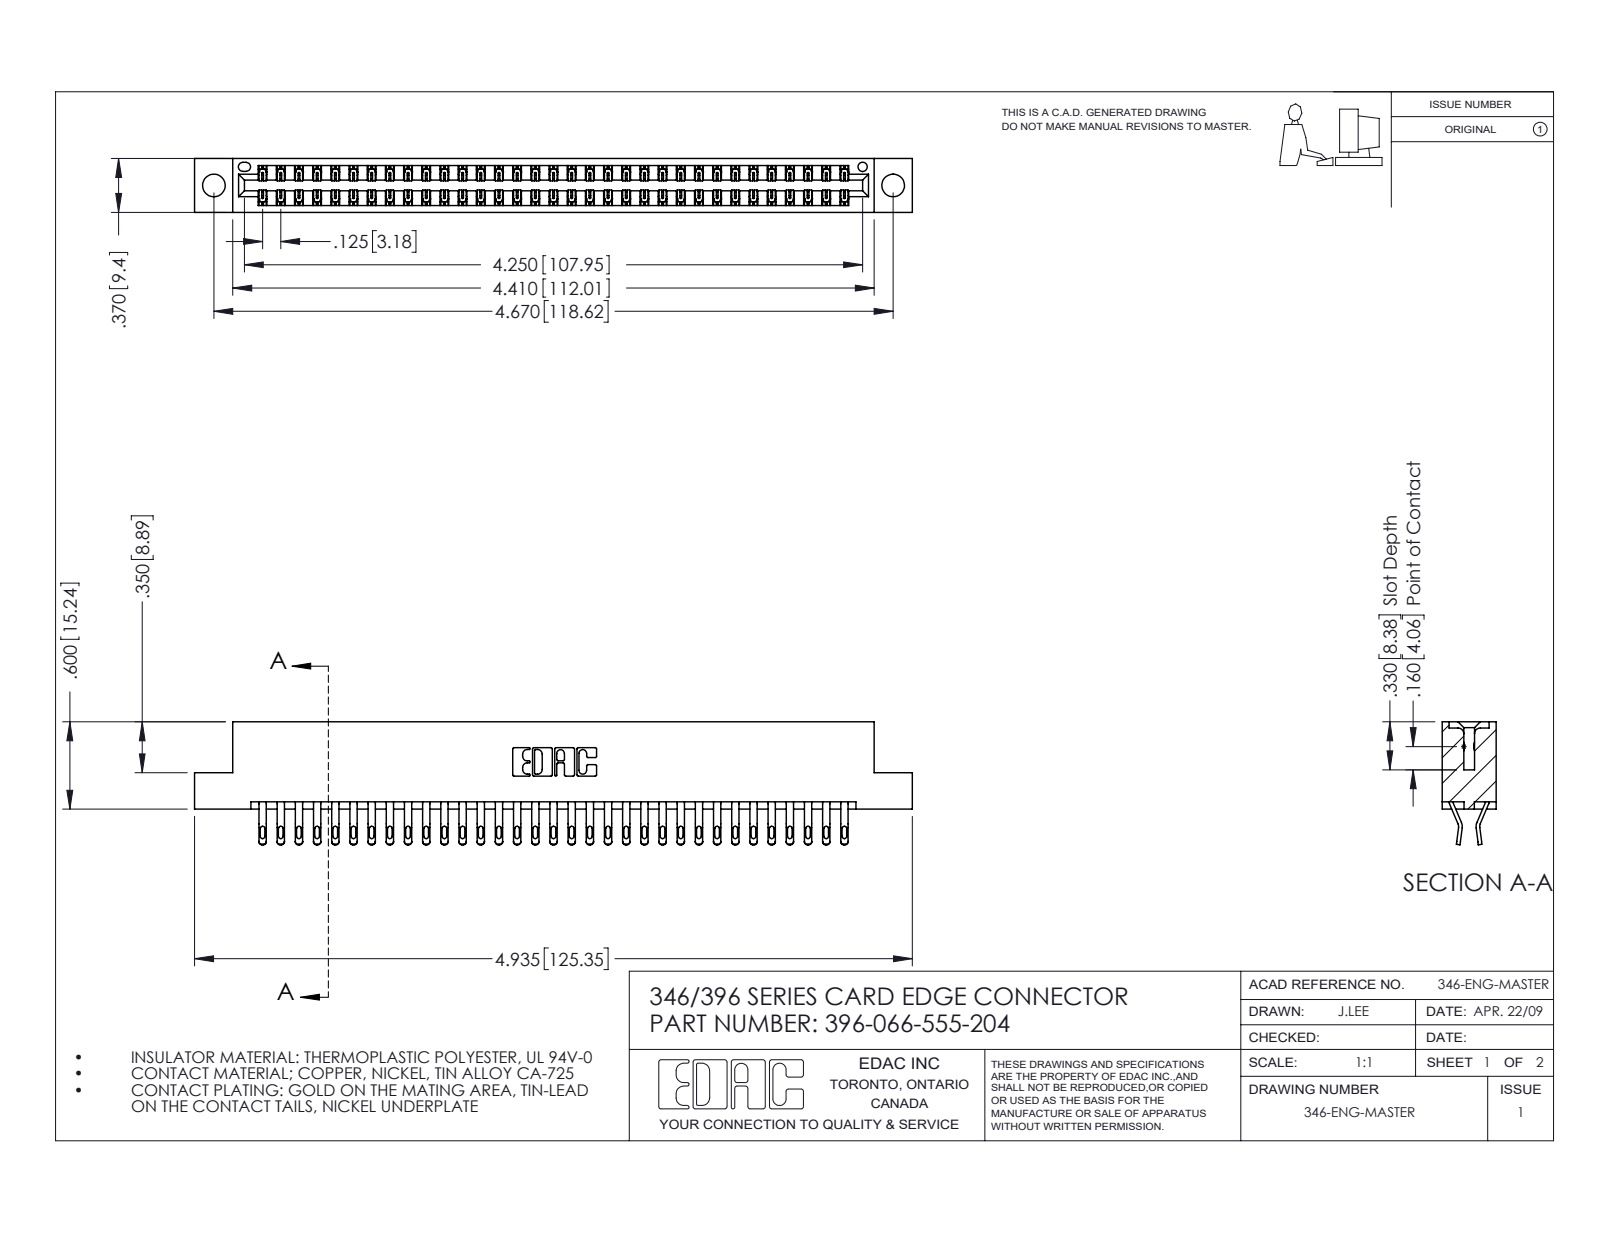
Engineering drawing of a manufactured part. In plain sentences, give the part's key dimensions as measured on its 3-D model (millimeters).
The part is named "346 Part_Flush Mounting Lugs - 0.156 Dia-TH; 396-066-555-204; 345-292-001_555 Tail". Its 3-D file was written by "SolidWorks 2016 (CONFIG_CONTROL_DESIGN)". It is 67 solids with 3950 faces: 2254 planar, 1696 cylindrical and 0 other. Overall it measures 125.3 by 21.5 by 9.4 millimeters. Its volume is 12 300 cubic millimeters and its surface area 17 200 square millimeters. Round holes: 2 of diameter 4, 1 of diameter 1.6. Partial cylindrical surfaces (rounded edges, fillets, slot ends): 132 of radius 0.4, 132 of radius 0.5, 99 of radius 0.2, 22 of radius 0.3, 6 of radius 0.2, 6 of radius 0.8, 3 of radius 0.7, 2 of radius 0.3. The main face-to-face distances are 1.2, 8.2, 9.4, 6.4, 0.6, 1.8, 7.6, 7, 3.8, 5.6. The hole center spacings are 6.2, 113.3, 118.6.
